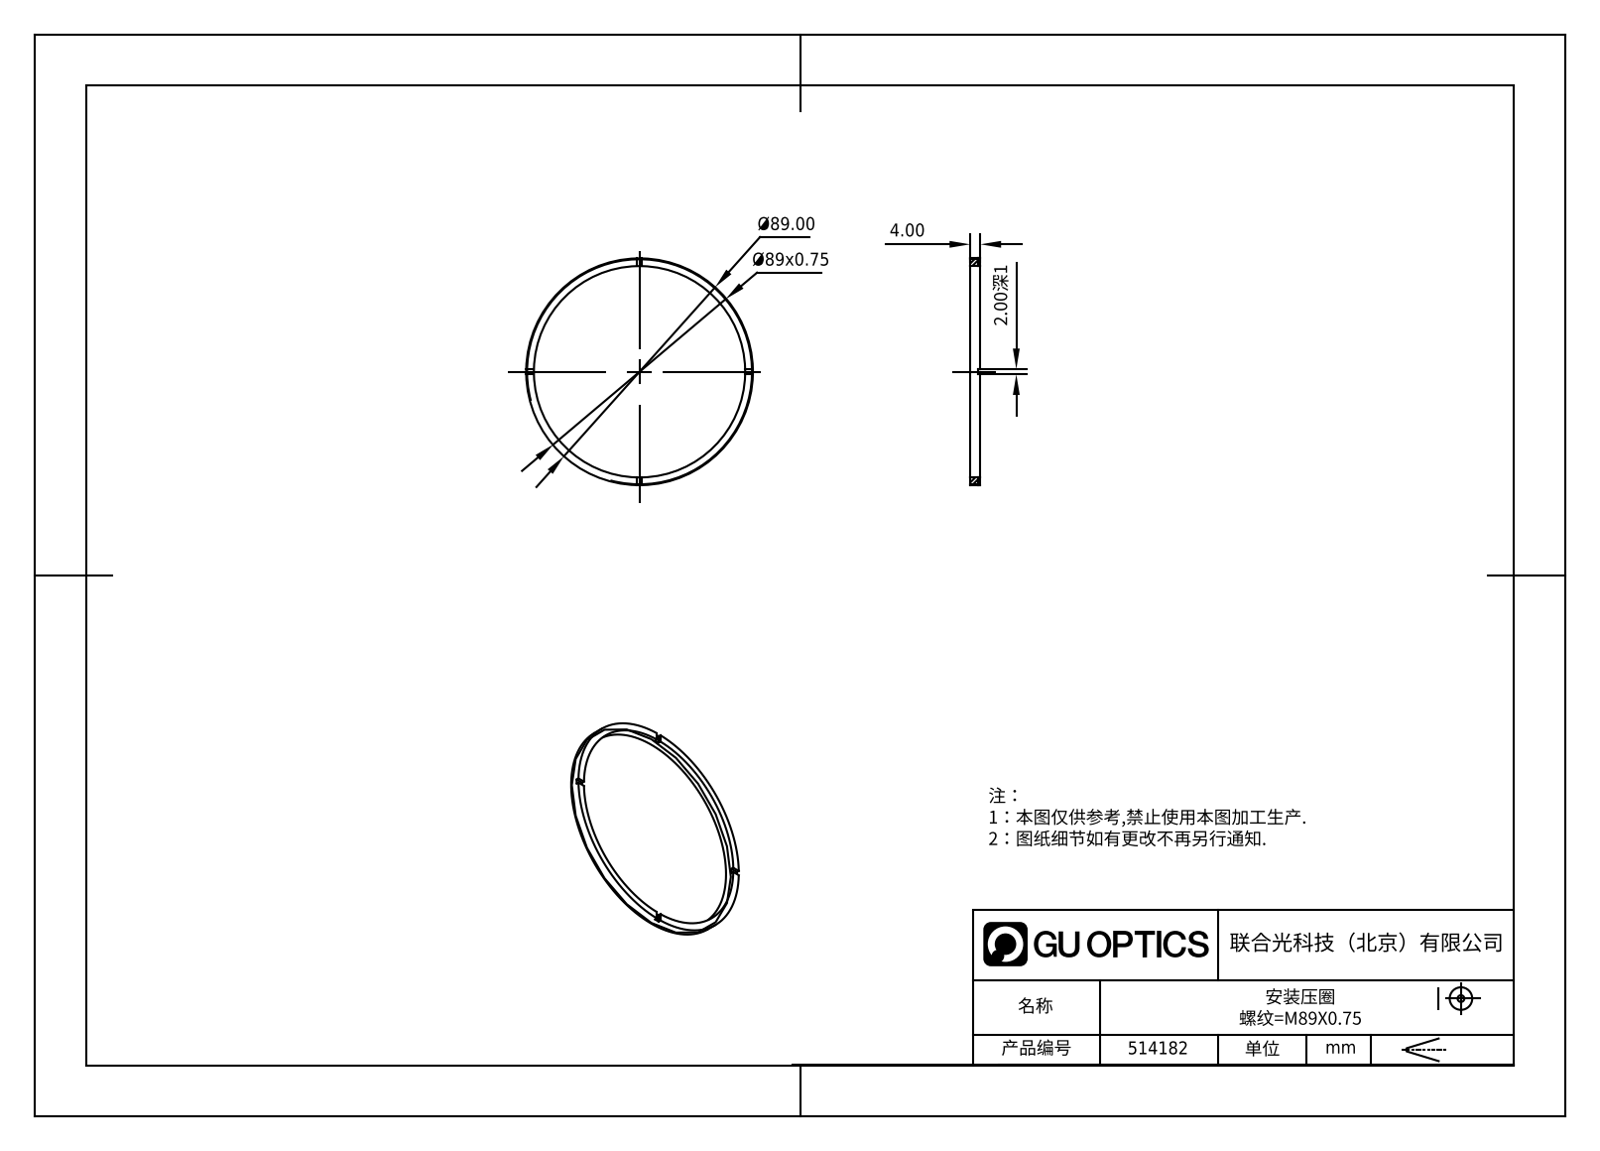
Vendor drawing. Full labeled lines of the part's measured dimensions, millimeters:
Part name (STEP PRODUCT): 514182
STEP written by: SolidWorks 2020 (CONFIG_CONTROL_DESIGN)
Units: millimetres
Bodies: 1 solid, 21 faces (17 planar, 4 cylindrical, 0 other)
Overall size (bounding box): 89 × 89 × 4
Volume: 3 218 mm³ · Surface area: 3 790 mm²
Round holes (diameter × count): ⌀83 ×1
Round bosses / shafts (diameter × count): ⌀89 ×1
Main face-to-face distances: 4, 3, 1, 2
